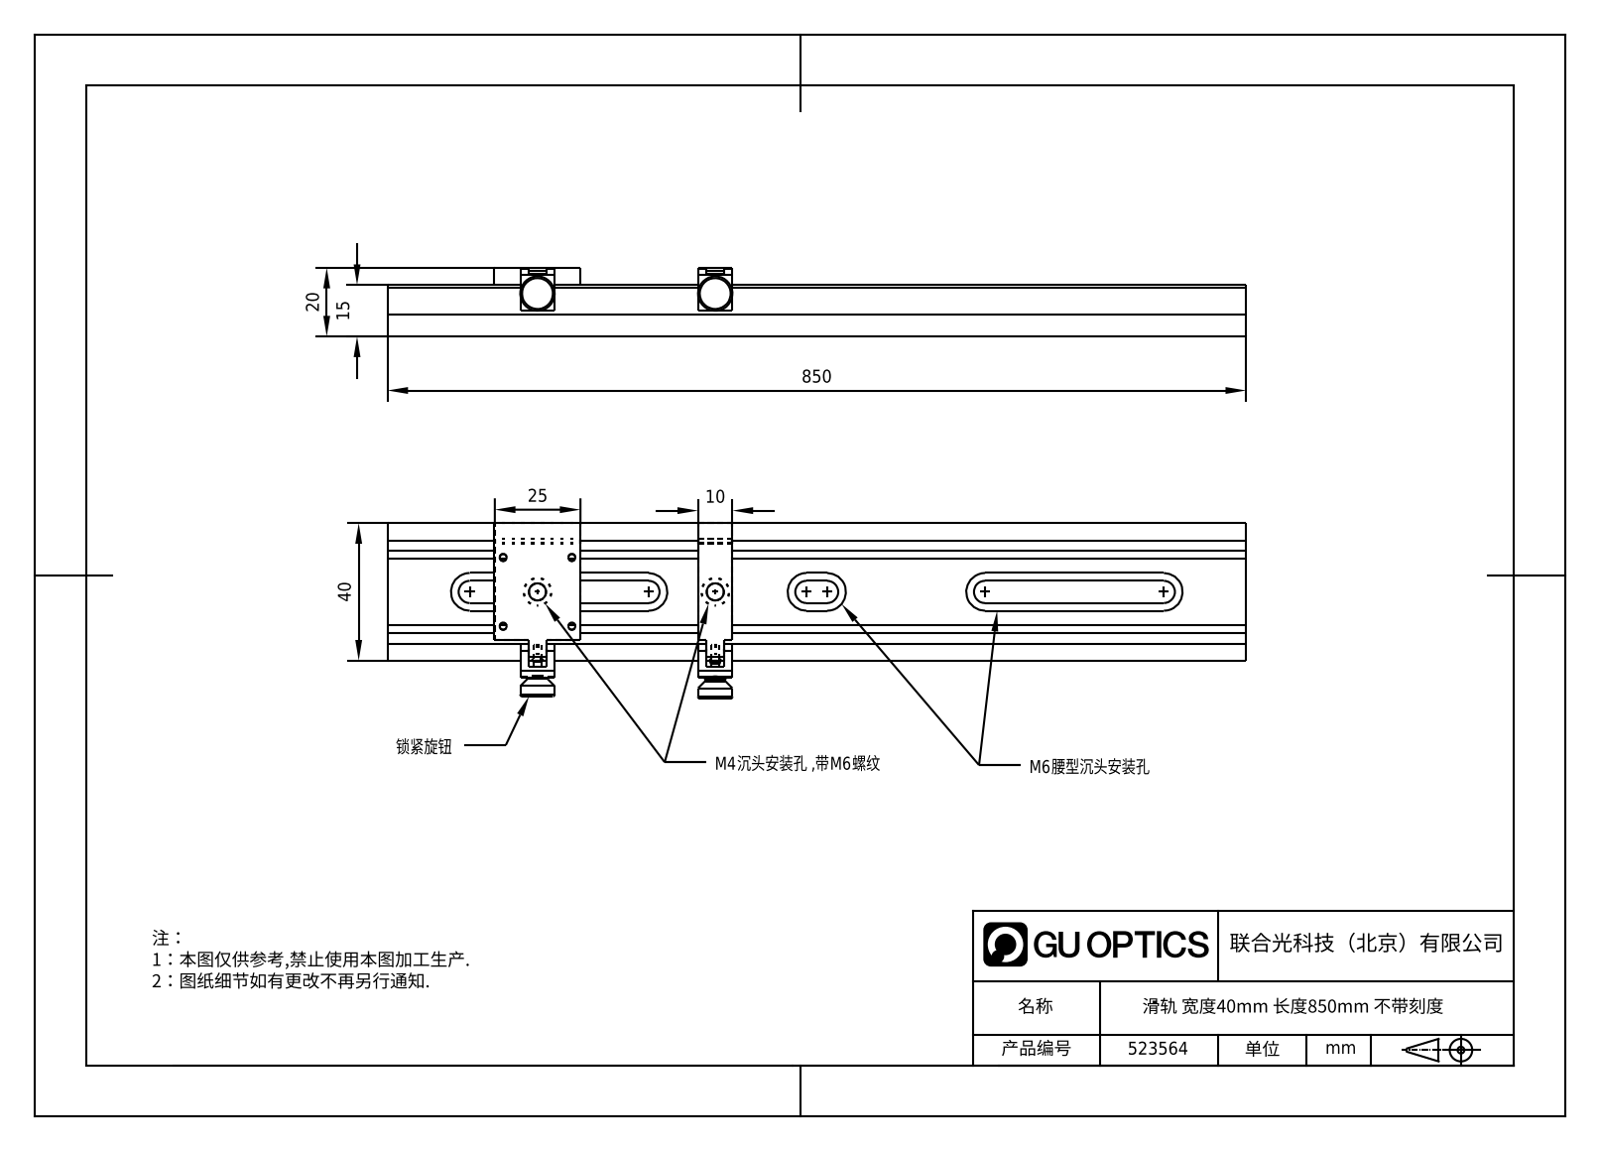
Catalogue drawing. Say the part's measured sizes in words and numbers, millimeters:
The part is named "4.2.1.21.1_40mm滑轨主体，长度850mm; 4.2.2.2，H40Z-25，40mm滑轨安装座，宽度25mm，A; 4.2.2.1.2，40mm滑轨安装座压块，宽度25mm，B; 4.2.2.1.1，40mm滑轨安装座主体，宽度10mm，A (+5 more)". Its 3-D file was written by "SolidWorks 2021 (CONFIG_CONTROL_DESIGN)". It is 8 solids with 275 faces: 140 planar, 107 cylindrical and 28 other. Overall it measures 850 by 51.03 by 20 millimeters. Its volume is 321 402 cubic millimeters and its surface area 117 980 square millimeters. Round holes: 4 of diameter 2.05, 2 of diameter 2.5, 2 of diameter 3.2, 2 of diameter 5, 2 of diameter 8, 1 of diameter 1.5, 1 of diameter 2. Round bosses or shafts: 2 of diameter 10, 2 of diameter 6, 2 of diameter 3, 2 of diameter 2.2. Partial cylindrical surfaces (rounded edges, fillets, slot ends): 18 of radius 3.25, 18 of radius 5.5, 1 of radius 1.25, 1 of radius 2.5, 1 of radius 4.5, 1 of radius 12.5. The main face-to-face distances are 6, 0.5, 14.5, 6.5, 15, 8.5, 40, 5, 8, 14. The hole center spacings are 14.14, 20, 18.6, 25.68, 28.28, 37.05.
